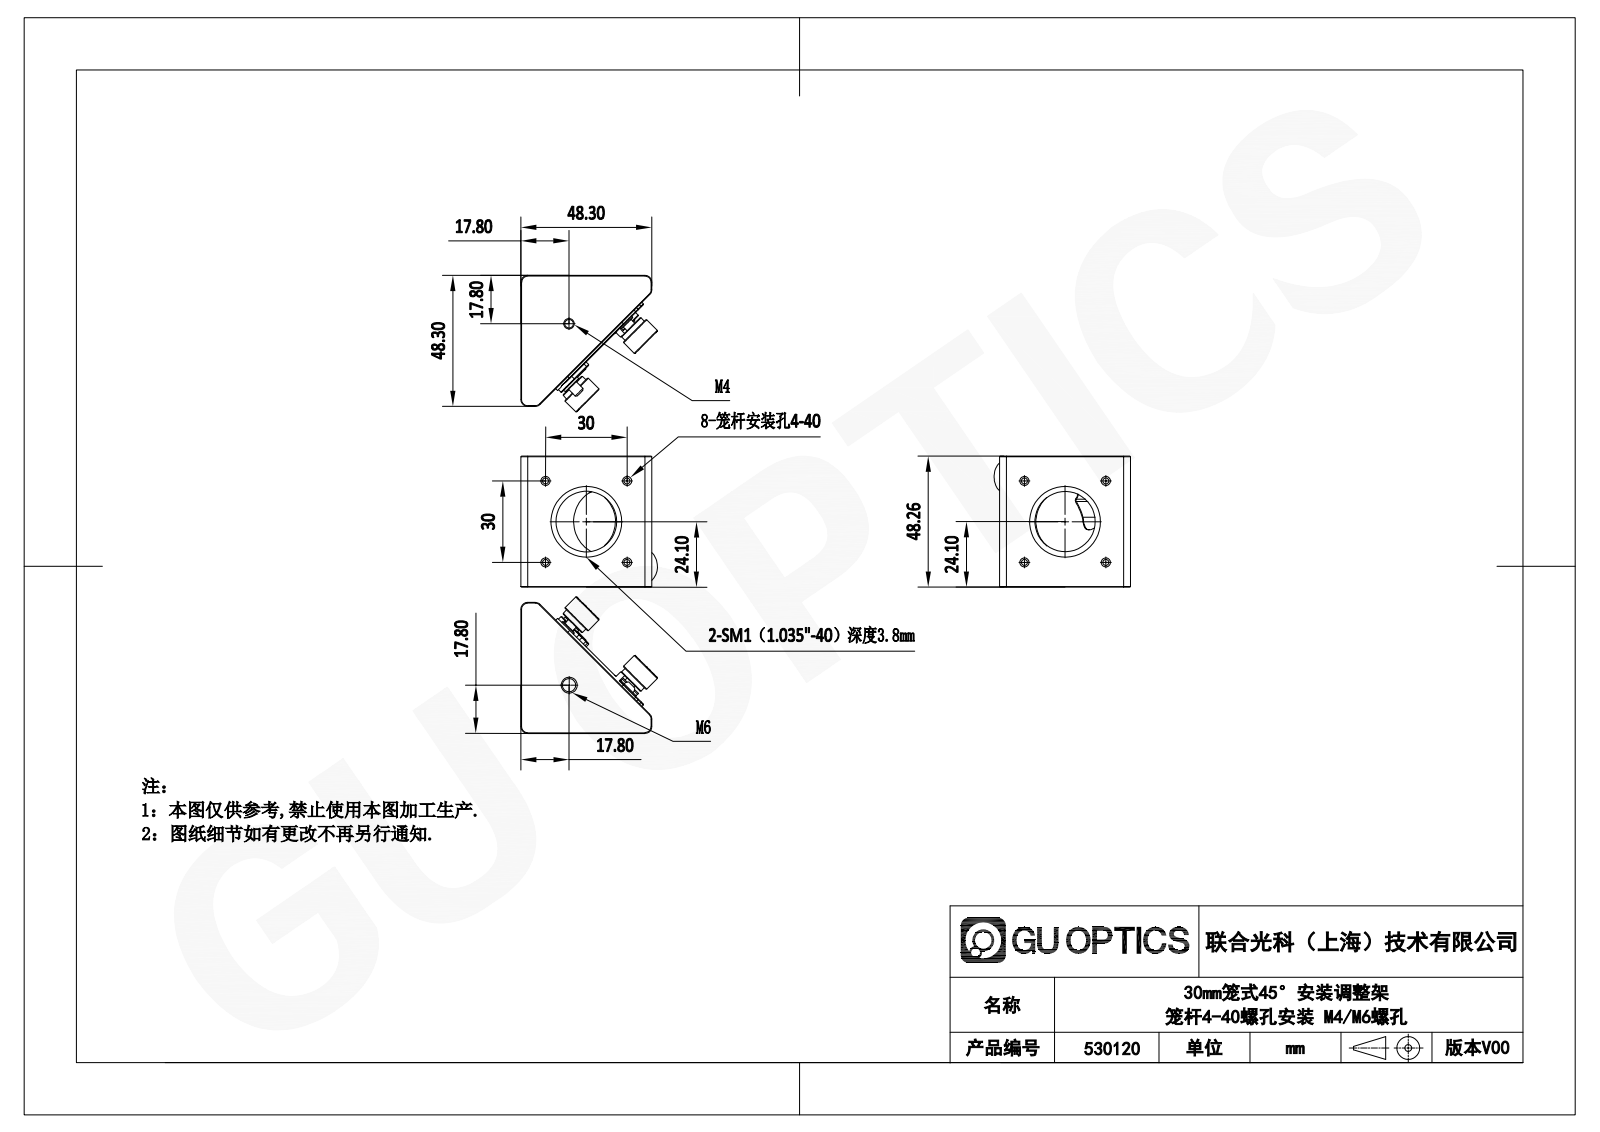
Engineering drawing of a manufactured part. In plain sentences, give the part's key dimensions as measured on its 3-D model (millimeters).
The part is named "530120". Its 3-D file was written by "SolidWorks 2020 (CONFIG_CONTROL_DESIGN)". It is 32 solids with 588 faces: 272 planar, 173 cylindrical and 143 other. Overall it measures 54.02 by 54.02 by 48.26 millimeters. Its volume is 49 093 cubic millimeters and its surface area 26 494 square millimeters. Round holes: 8 of diameter 2.26, 3 of diameter 2.9, 3 of diameter 2.99, 3 of diameter 3.5, 3 of diameter 3.56, 3 of diameter 3.7, 3 of diameter 3.75, 3 of diameter 7, 2 of diameter 1.6, 2 of diameter 2.4, 2 of diameter 2.8, 2 of diameter 4. Round bosses or shafts: 5 of diameter 1.5, 3 of diameter 12, 3 of diameter 10, 3 of diameter 4, 3 of diameter 2, 2 of diameter 6.8, 2 of diameter 6, 2 of diameter 5.5. Partial cylindrical surfaces (rounded edges, fillets, slot ends): 30 of radius 0.79, 7 of radius 1, 6 of radius 0.93, 5 of radius 2.54, 4 of radius 0.79, 4 of radius 1.27, 4 of radius 4.32, 4 of radius 6.35. The main face-to-face distances are 1.14, 48.26, 4.14, 3, 10.11, 7.11, 5.97, 8.38, 5.38, 4.24. The hole center spacings are 22.81, 30, 33.02, 34.38, 36.9, 45.63, 5.46, 25.18.
